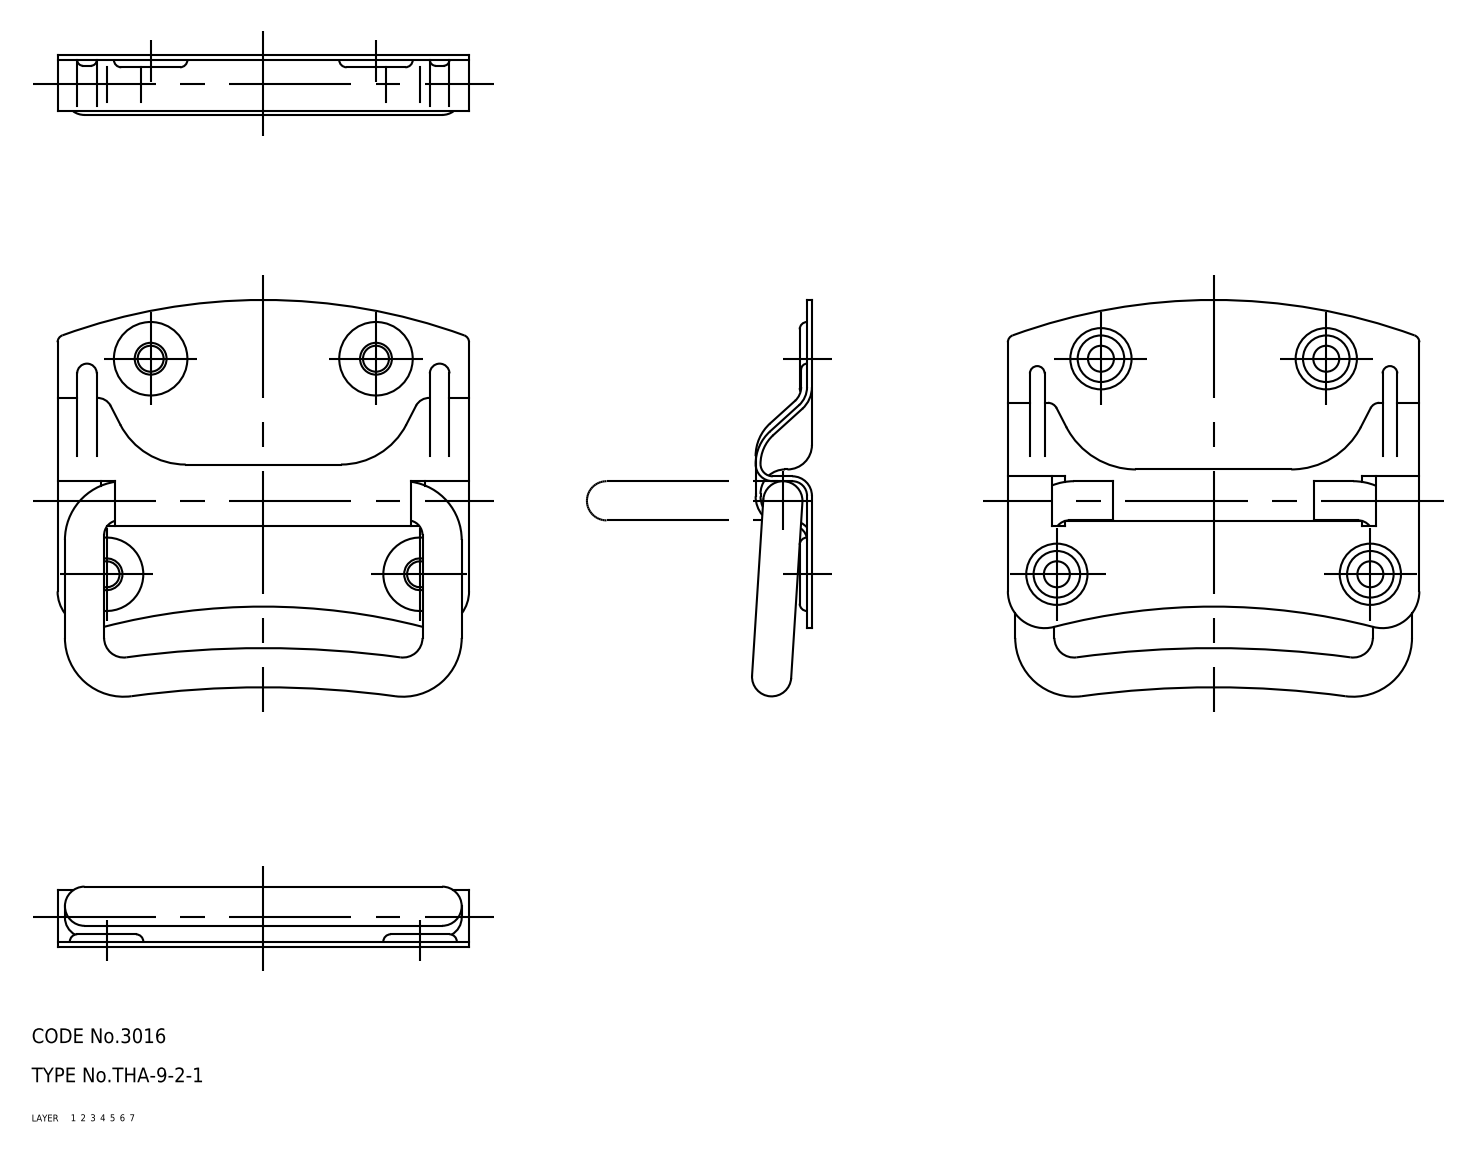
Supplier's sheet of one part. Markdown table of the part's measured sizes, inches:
| quantity | value |
| --- | --- |
| part name | grip; base; THA_9_2_1_3431_36 |
| STEP written by | CADfix (AUTOMOTIVE_DESIGN) |
| units | inches |
| bodies | 2 solids, 260 faces (0 planar, 0 cylindrical, 260 other) |
| overall size | 3.307 × 3.189 × 0.482 |
| volume | 0.891 in³ |
| surface area | 27.13 in² |
